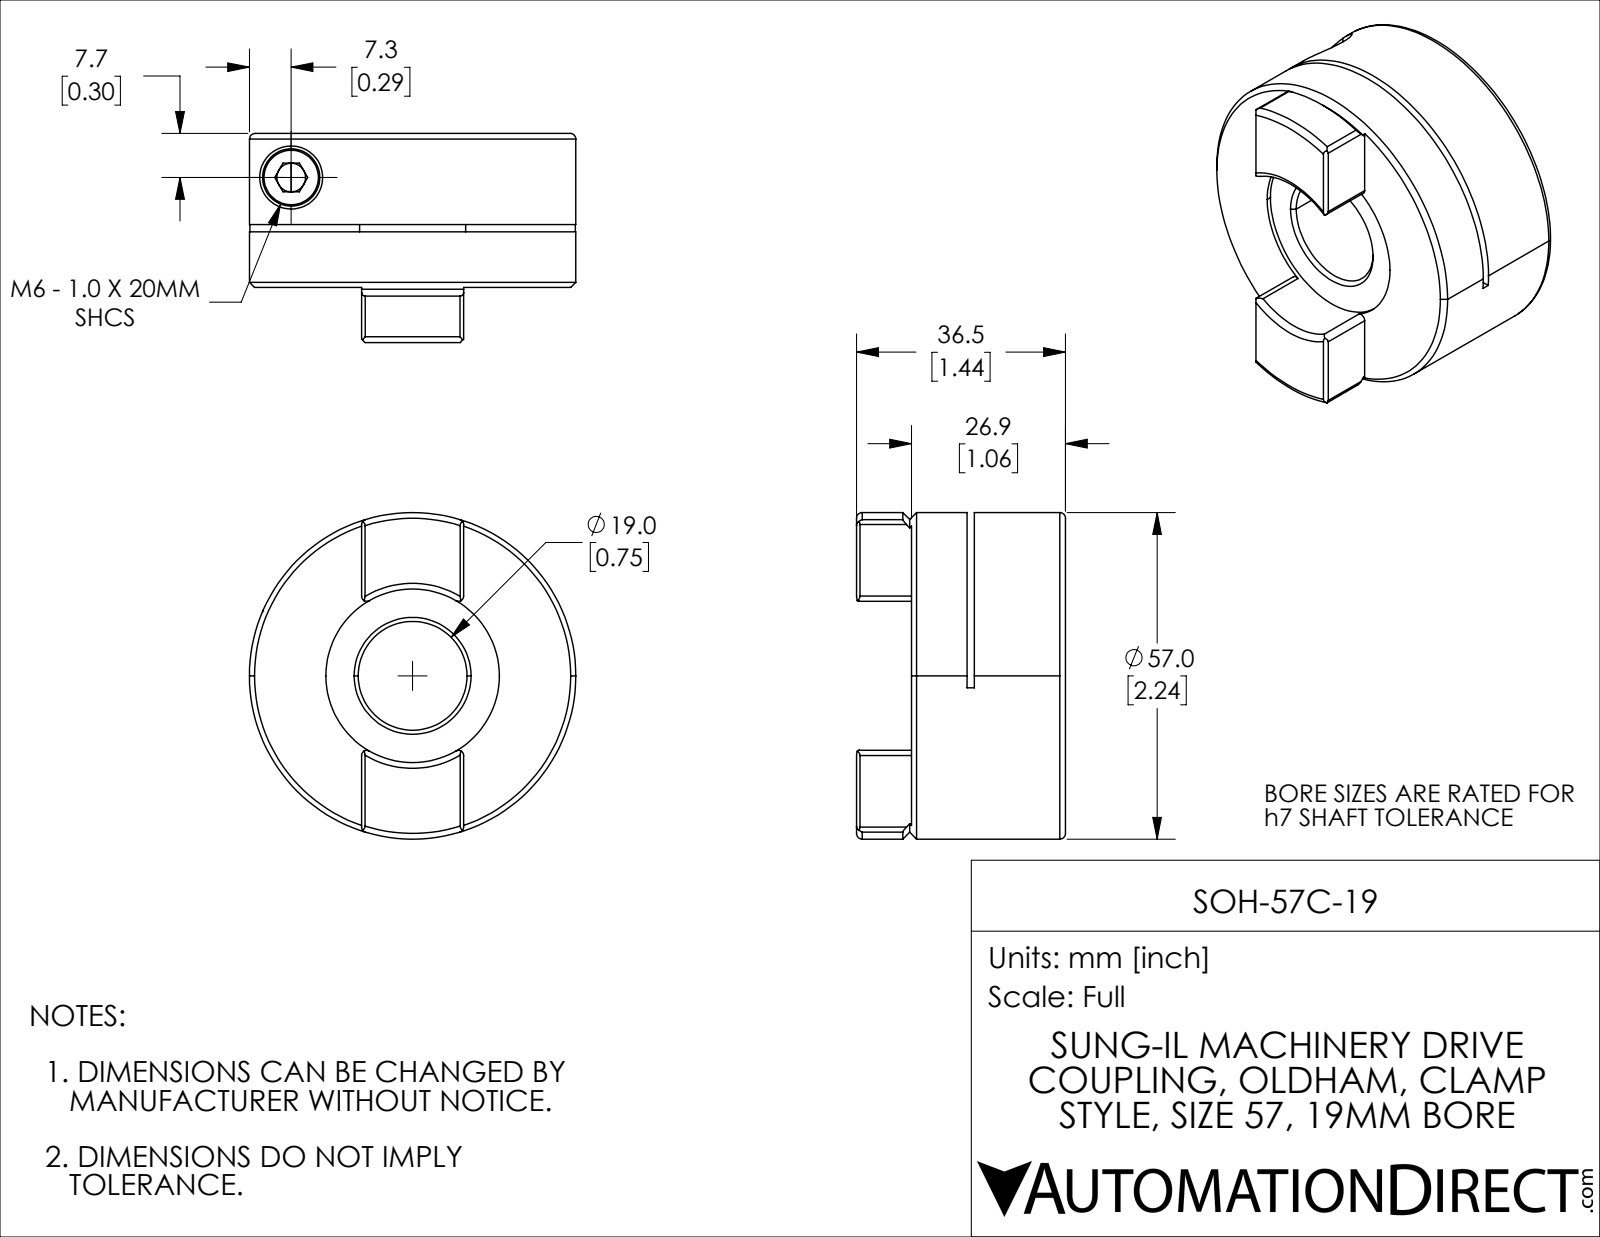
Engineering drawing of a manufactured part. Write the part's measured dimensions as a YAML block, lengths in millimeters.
part_name: "SOH-57C-19"
step_written_by: "SolidWorks 2021 (CONFIG_CONTROL_DESIGN)"
units: millimeters
bodies: {solids: 2, faces: 97, planar: 39, cylindrical: 33, other: 25}
overall_size: [57, 57, 36.5]
volume: 62267
surface_area: 16431
round_holes:
  - {diameter: 5, count: 1}
  - {diameter: 6.4, count: 1}
  - {diameter: 11, count: 1}
  - {diameter: 19, count: 1}
  - {diameter: 30.3, count: 1}
round_bosses_or_shafts:
  - {diameter: 57, count: 1}
  - {diameter: 10, count: 1}
  - {diameter: 6, count: 1}
partial_cylinders:
  - {radius: 0.9, count: 8}
  - {radius: 40, count: 1}
face_to_face_distances: [1.3, 26.9, 17.2, 9.7, 15.9, 11, 10.2, 26.1, 8.9, 0.8]
